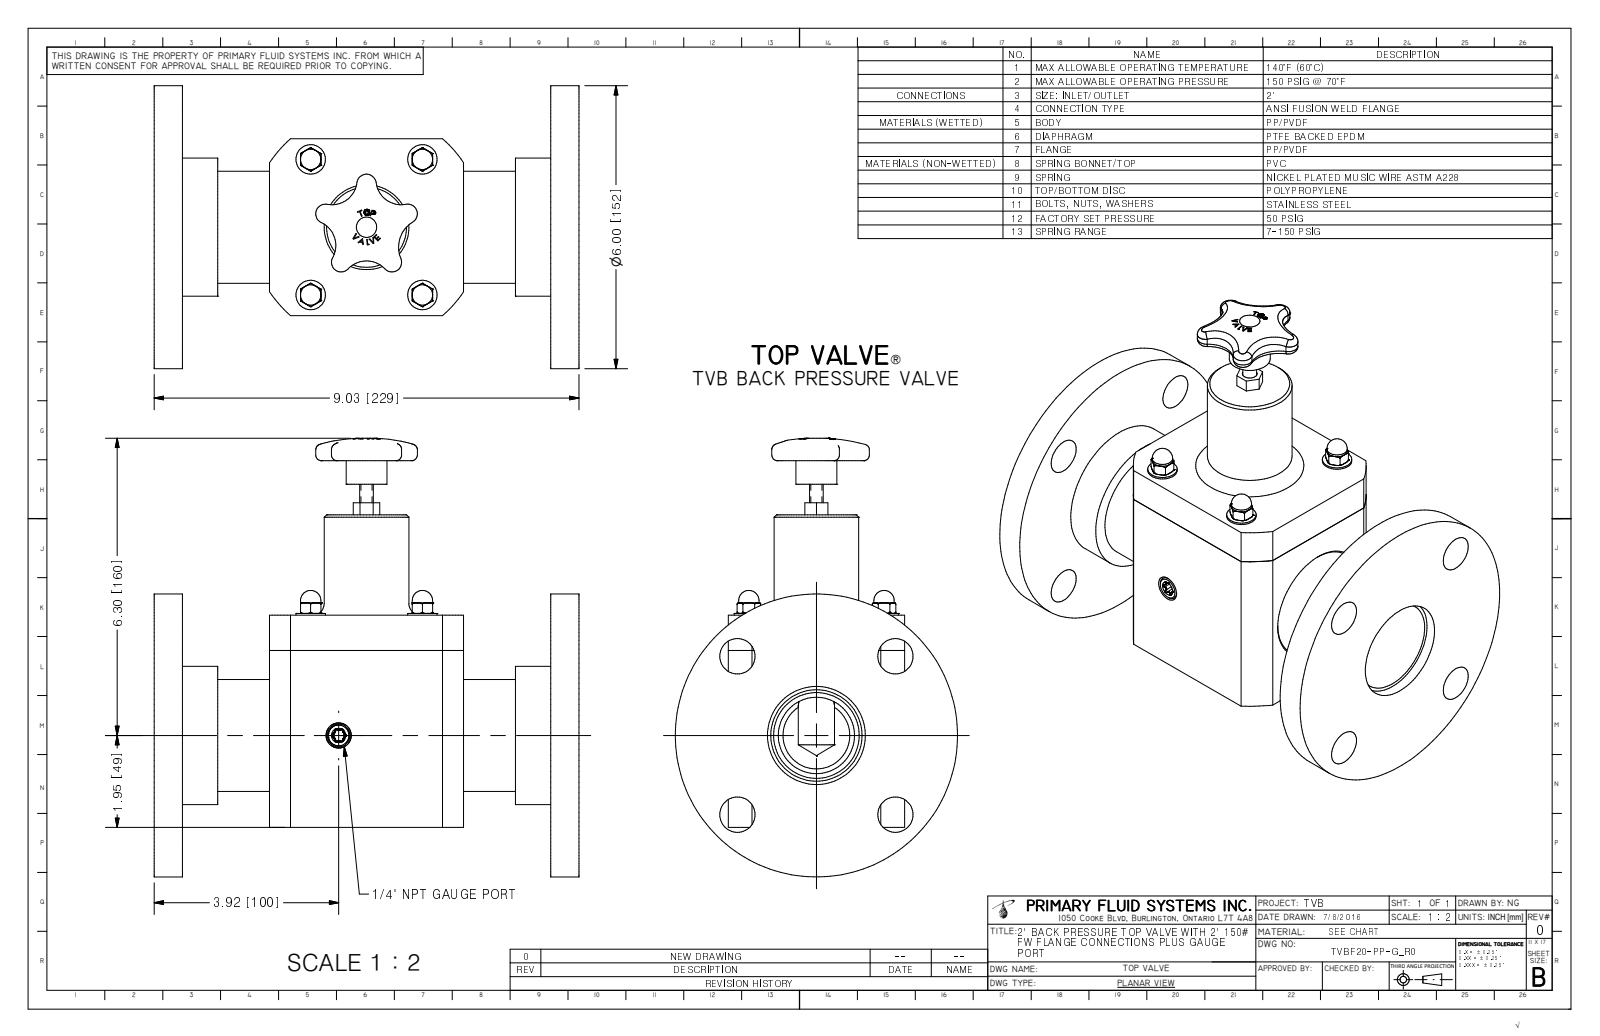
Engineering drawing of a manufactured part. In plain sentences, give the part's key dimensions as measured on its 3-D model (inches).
The part is named "TVBF20-PP-G_R0". Its 3-D file was written by "Autodesk Inventor 2009 (AUTOMOTIVE_DESIGN)". It is 1 solid with 383 faces: 160 planar, 67 cylindrical and 156 other. Overall it measures 9.302 by 9.03 by 6 inches. Its volume is 106.9 cubic inches and its surface area 316.8 square inches. Round holes: 4 of diameter 0.175, 4 of diameter 0.75, 1 of diameter 1.939, 1 of diameter 2.08. Round bosses or shafts: 4 of diameter 0.625, 4 of diameter 0.433, 4 of diameter 0.375, 1 of diameter 6, 1 of diameter 2.93, 1 of diameter 2.375, 1 of diameter 1.8, 1 of diameter 0.87. Partial cylindrical surfaces (rounded edges, fillets, slot ends): 6 of radius 0.027, 5 of radius 0.085, 5 of radius 0.205, 4 of radius 0.536, 4 of radius 0.656, 1 of radius 0.625, 1 of radius 0.745, 1 of radius 2.475. The main face-to-face distances are 0.6, 8.43, 9.03, 7.83, 2.452, 6.578, 1.852, 5.978, 3.75, 4.5. The hole center spacings are 2.375, 3.359, 2.375, 2.875, 3.729, 4.75.
